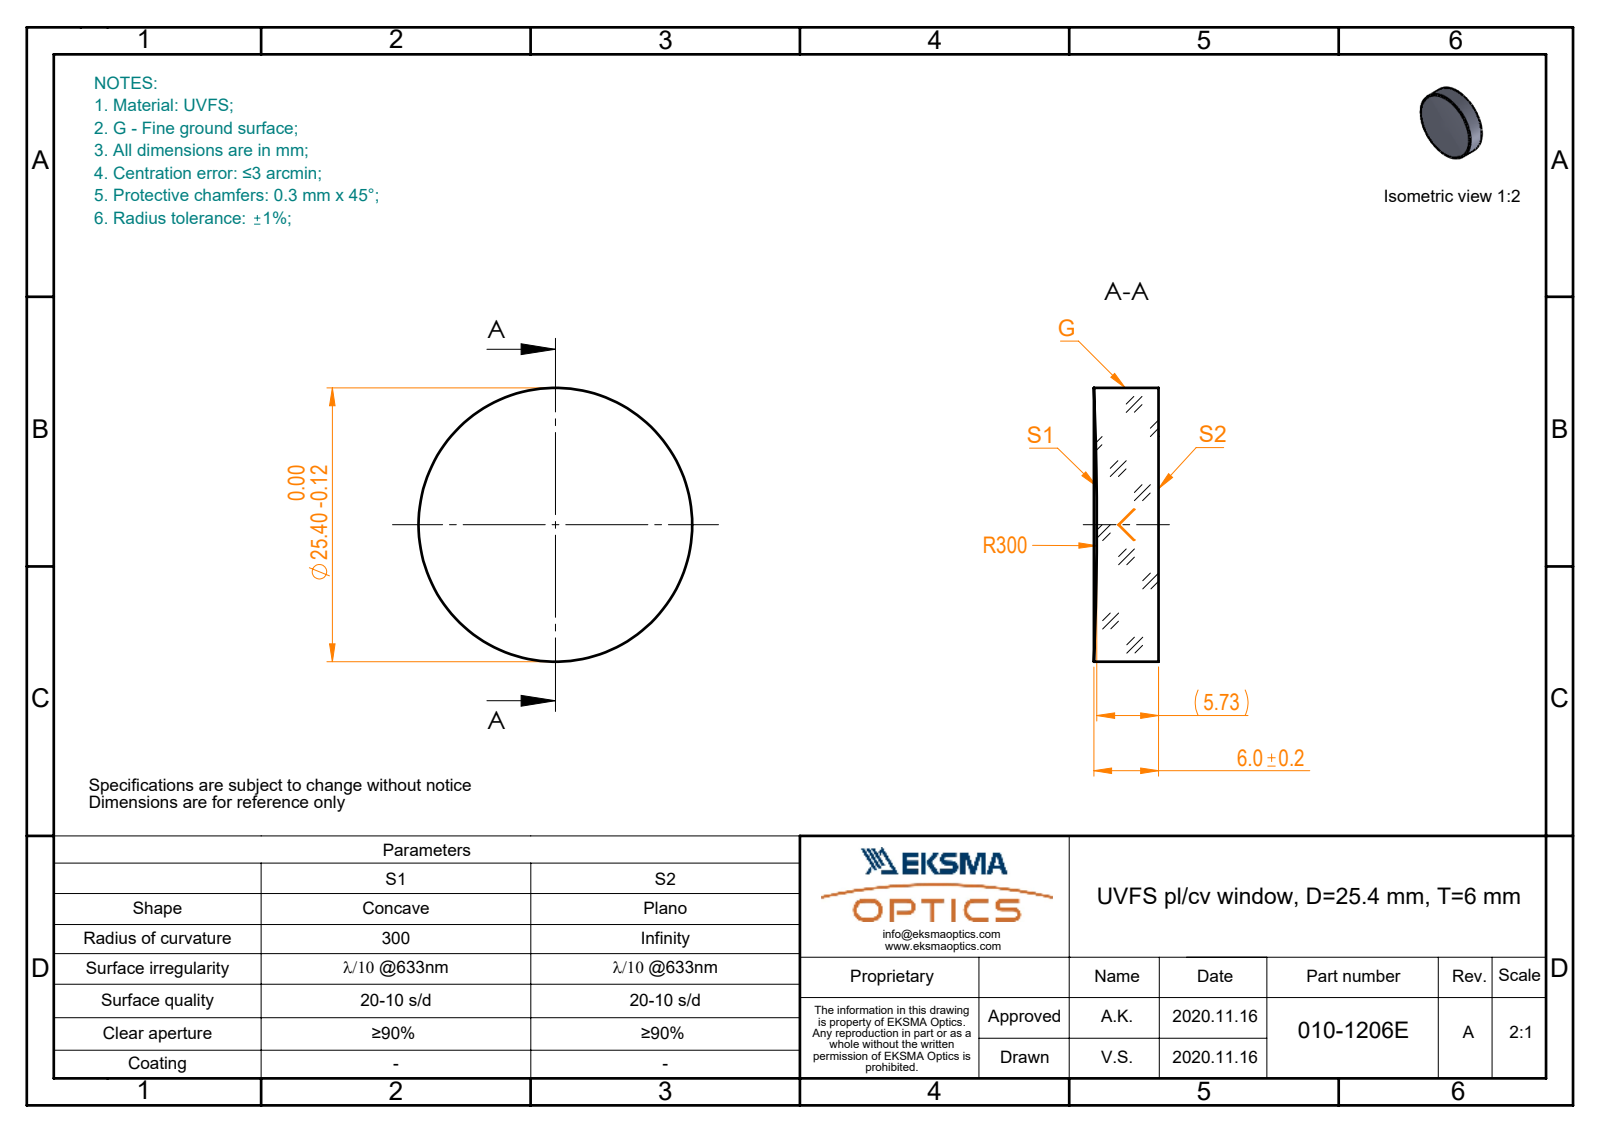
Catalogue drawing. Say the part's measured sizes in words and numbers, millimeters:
The part is named "010-1206E_UVFS_PCV_window". Its 3-D file was written by "SolidWorks 2019 (CONFIG_CONTROL_DESIGN)". It is 1 solid with 5 faces: 1 planar, 2 cylindrical and 2 other. Overall it measures 25.4 by 25.4 by 6 millimeters. Its volume is 2 972 cubic millimeters and its surface area 1 492 square millimeters. Round bosses or shafts: 1 of diameter 25.4.
